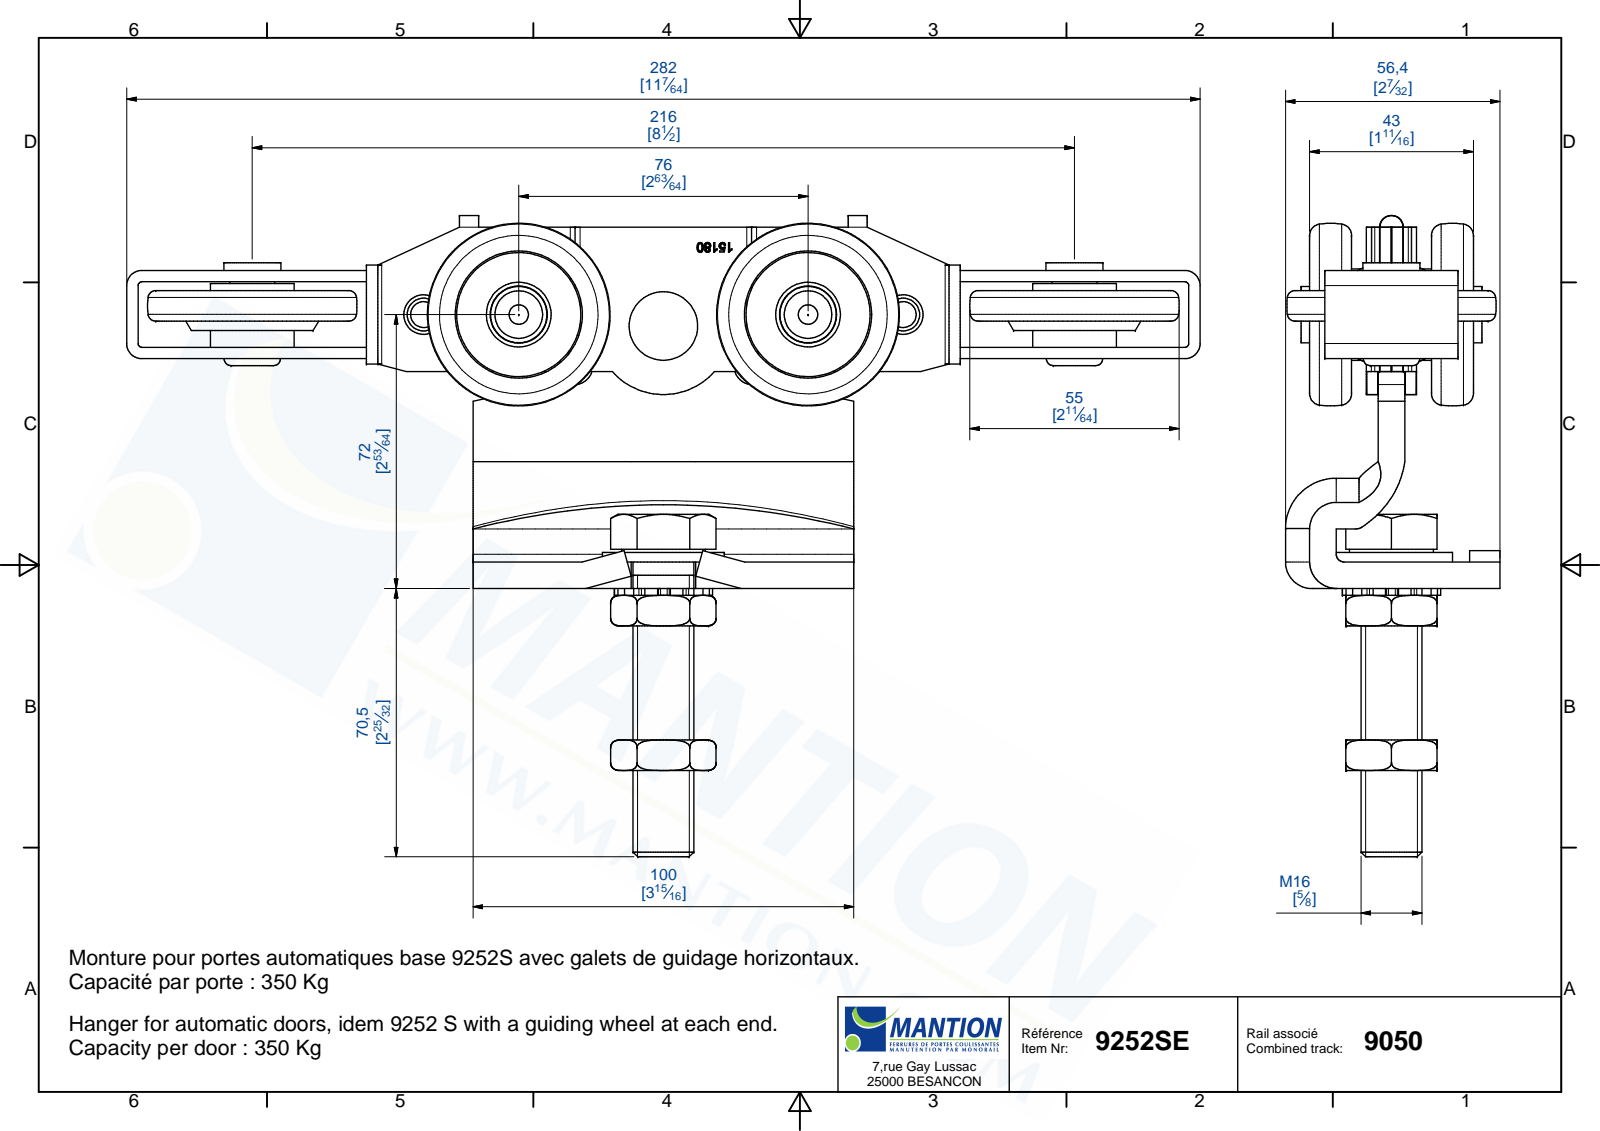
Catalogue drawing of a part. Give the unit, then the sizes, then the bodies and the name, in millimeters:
Units: millimetres
Overall size (bounding box): 282 × 168.55 × 56.35
Round holes (diameter × count): ⌀12.5 ×4, ⌀1.46 ×2, ⌀5.2 ×2, ⌀11.8 ×2, ⌀12 ×2, ⌀12.2 ×2, ⌀15 ×2, ⌀16.3 ×2, ⌀27 ×2, ⌀33.4 ×2, ⌀13.84 ×1, ⌀16.2 ×1
Round bosses / shafts (diameter × count): ⌀3.38 ×4, ⌀22 ×3, ⌀32.6 ×2, ⌀25 ×2, ⌀24 ×2, ⌀15 ×2, ⌀14.8 ×2, ⌀10.4 ×2
Partial cylindrical surfaces — rounded edges, fillets, slot ends (radius × count): R1.3 ×64, R0.48 ×24, R1 ×12, R2 ×10, R13 ×5, R1.81 ×4, R4 ×4, R4.68 ×4
Main face-to-face distances: 3, 3.5, 6.6, 3.1, 7, 3.6, 6.5, 3.4, 2.9, 0.5
Hole centre spacings: 25, 25.74, 29.29, 38.12, 51.37, 55.87, 63.07, 79.94
Volume: 328 928 mm³ · Surface area: 176 568 mm²
Bodies: 33 solids, 966 faces (519 planar, 288 cylindrical, 159 other)
Part name (STEP PRODUCT): 9252SE; 9252; 15180; 15709_A (+8 more)
STEP written by: Autodesk Inventor 2017 (AUTOMOTIVE_DESIGN)
